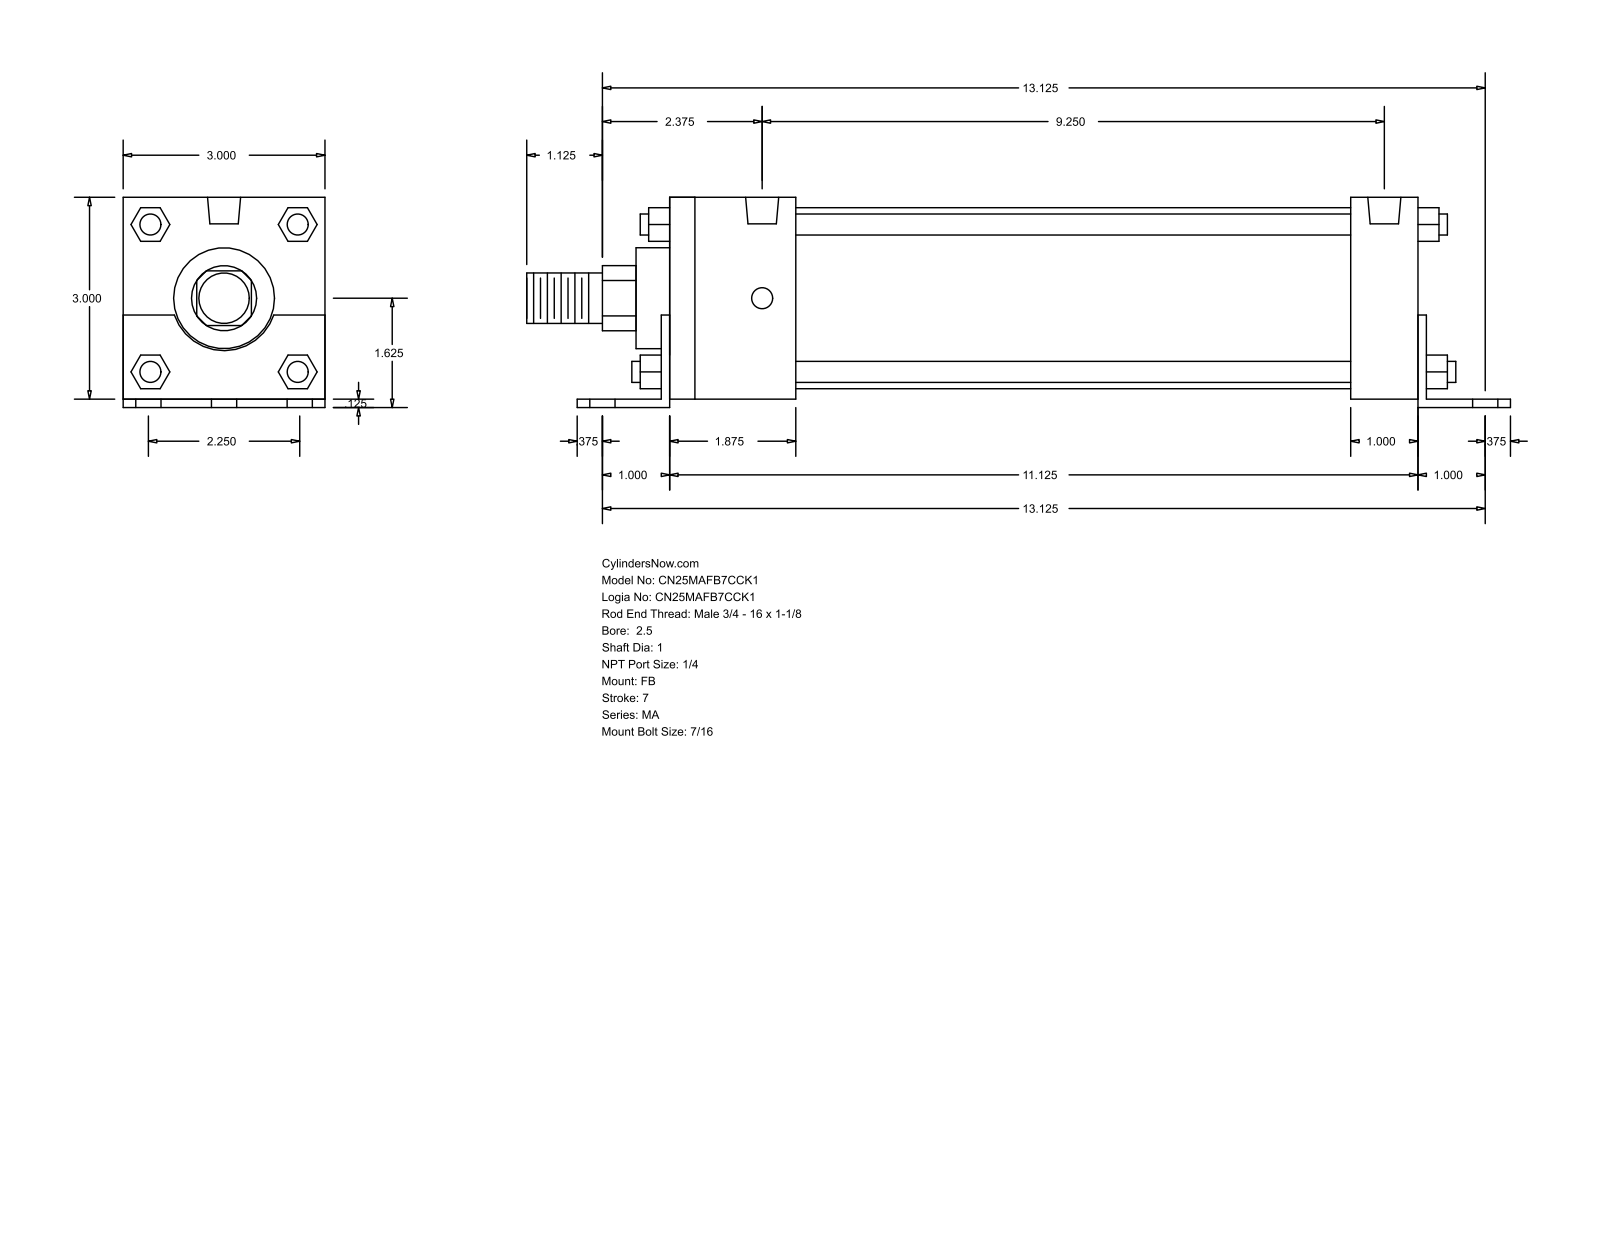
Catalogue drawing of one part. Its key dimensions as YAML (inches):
part_name: "MA_FB__0250_1"
step_written_by: "GSSL Pune (CONFIG_CONTROL_DESIGN)"
units: inches
bodies: {solids: 0, faces: 140, planar: 105, cylindrical: 35, other: 0}
overall_size: [14.625, 3.125, 3]
round_holes:
  - {diameter: 0.437, count: 6}
  - {diameter: 0.313, count: 4}
  - {diameter: 0.492, count: 2}
round_bosses_or_shafts:
  - {diameter: 0.313, count: 4}
  - {diameter: 2.69, count: 1}
  - {diameter: 1.5, count: 1}
  - {diameter: 1, count: 1}
  - {diameter: 0.75, count: 1}
partial_cylinders:
  - {radius: 0.484, count: 1}
  - {radius: 0.78, count: 1}
face_to_face_distances: [3, 0.125, 3.125, 11.25, 11.125, 0.5, 2, 1.875, 9.25, 9.375]
hole_center_spacings: [1.125, 13.173, 13.125, 1.875, 2.25, 2.628, 9.25, 10.809]
